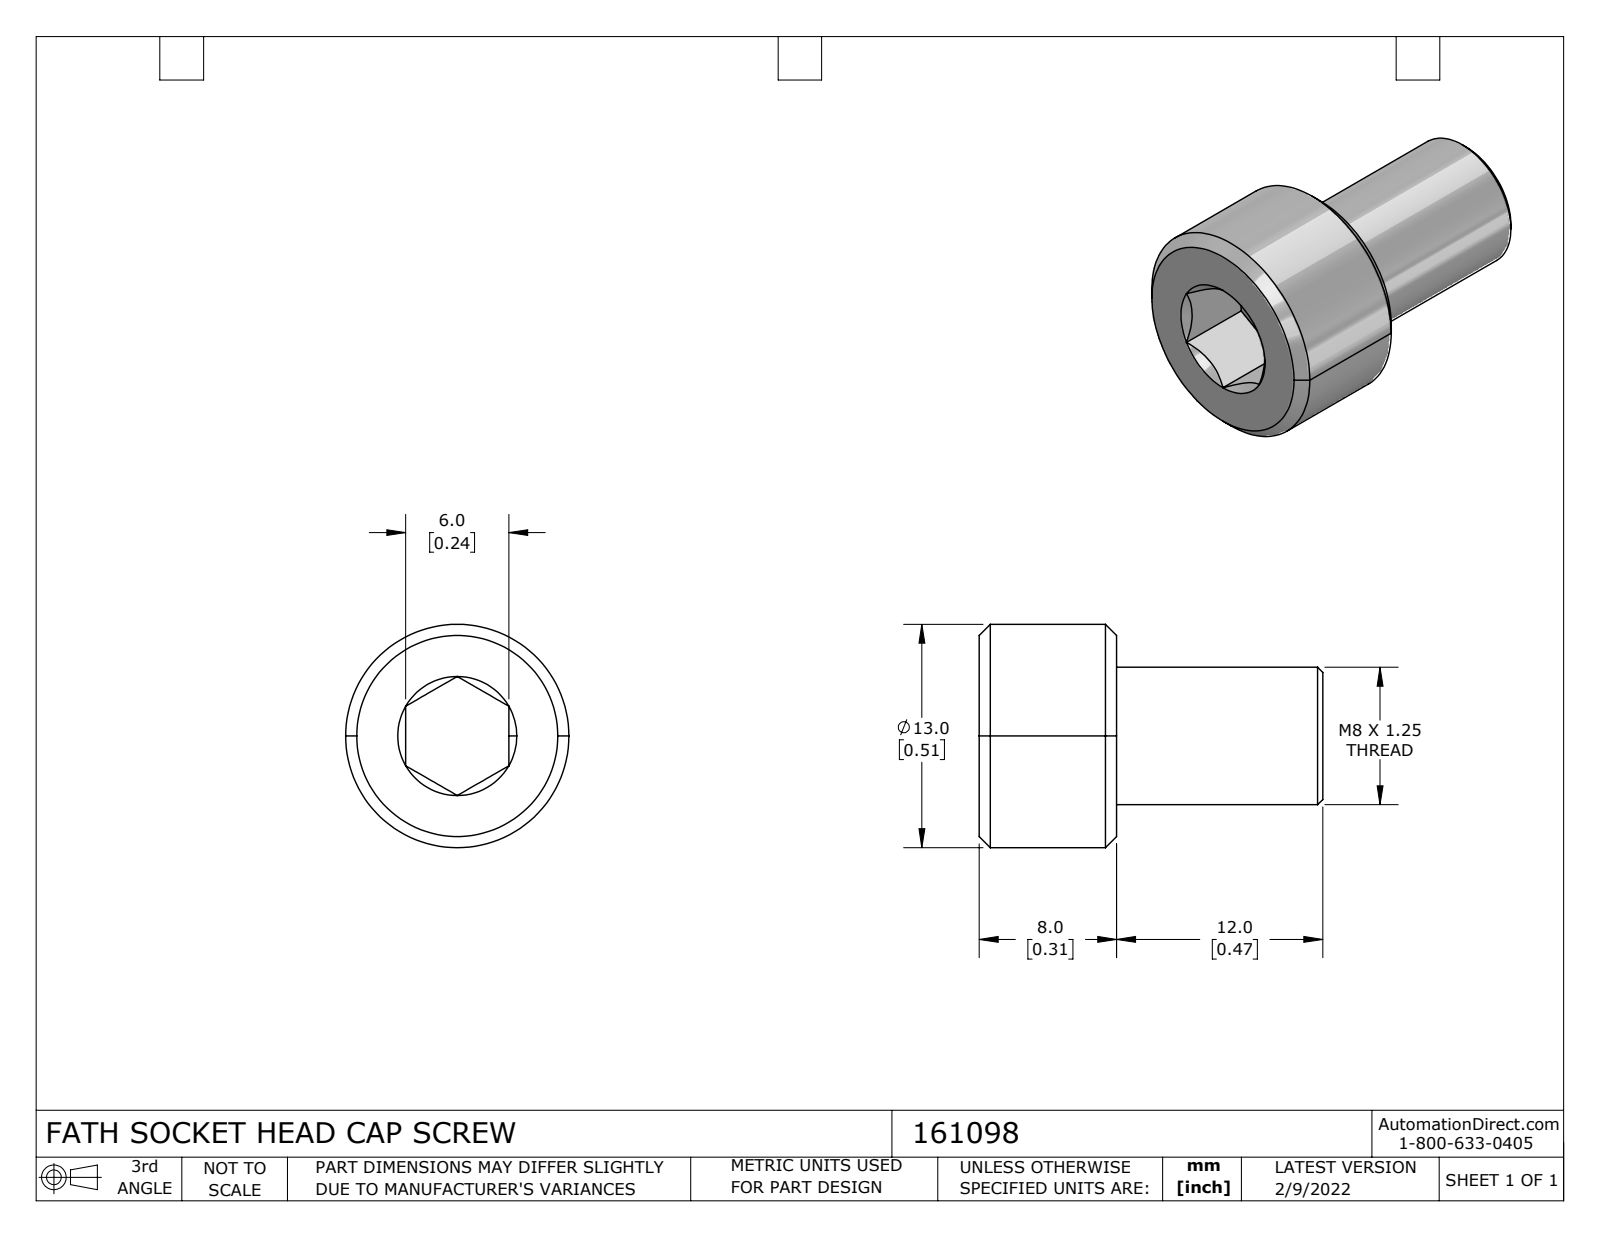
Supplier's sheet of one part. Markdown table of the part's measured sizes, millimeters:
| quantity | value |
| --- | --- |
| part name | 161098 |
| STEP written by | SolidWorks 2021 (CONFIG_CONTROL_DESIGN) |
| units | millimeters |
| bodies | 1 solid, 27 faces (10 planar, 4 cylindrical, 13 other) |
| overall size | 20 × 13 × 13 |
| volume | 1 506 mm³ |
| surface area | 947 mm² |
| round bosses / shafts (diameter × count) | 13 × 1, 8 × 1 |
| main face-to-face distances | 8, 6, 20, 12, 4.5, 3.5, 15.5 |
